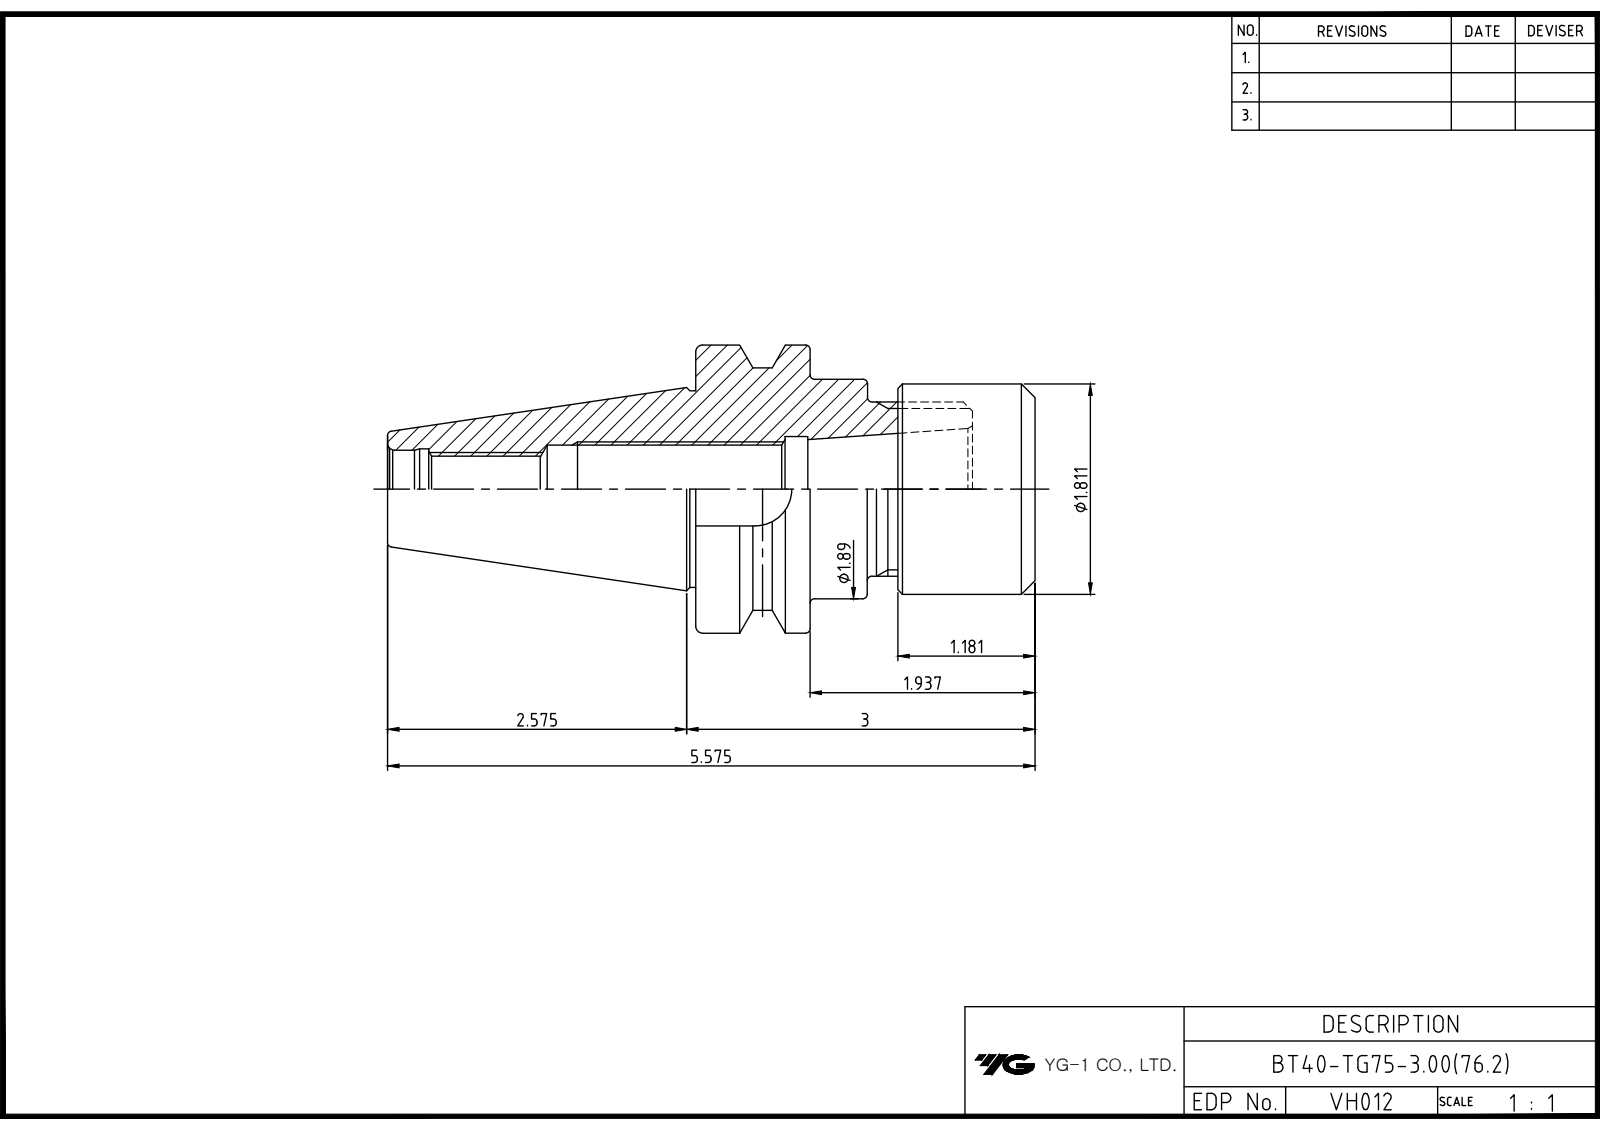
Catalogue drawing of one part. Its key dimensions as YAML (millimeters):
part_name: "BT40-TG75-76.2; LO-BT40-TG75-76.2; TG75 NUT"
step_written_by: "Autodesk Inventor 2022 (AUTOMOTIVE_DESIGN)"
units: millimeters
bodies: {solids: 2, faces: 61, planar: 21, cylindrical: 18, other: 22}
overall_size: [141.6, 63, 63]
volume: 166237
surface_area: 39564
round_holes:
  - {diameter: 13.84, count: 1}
  - {diameter: 17, count: 1}
  - {diameter: 17.6, count: 1}
  - {diameter: 18.92, count: 1}
  - {diameter: 23, count: 1}
  - {diameter: 26.67, count: 1}
  - {diameter: 38.1, count: 1}
round_bosses_or_shafts:
  - {diameter: 63, count: 1}
  - {diameter: 52.6, count: 1}
  - {diameter: 48, count: 1}
  - {diameter: 46, count: 1}
  - {diameter: 44, count: 1}
partial_cylinders:
  - {radius: 8.05, count: 1}
face_to_face_distances: [25, 60.5, 35.5, 74.2, 49.2, 13.7, 37.5, 12.5, 23, 36.7]
